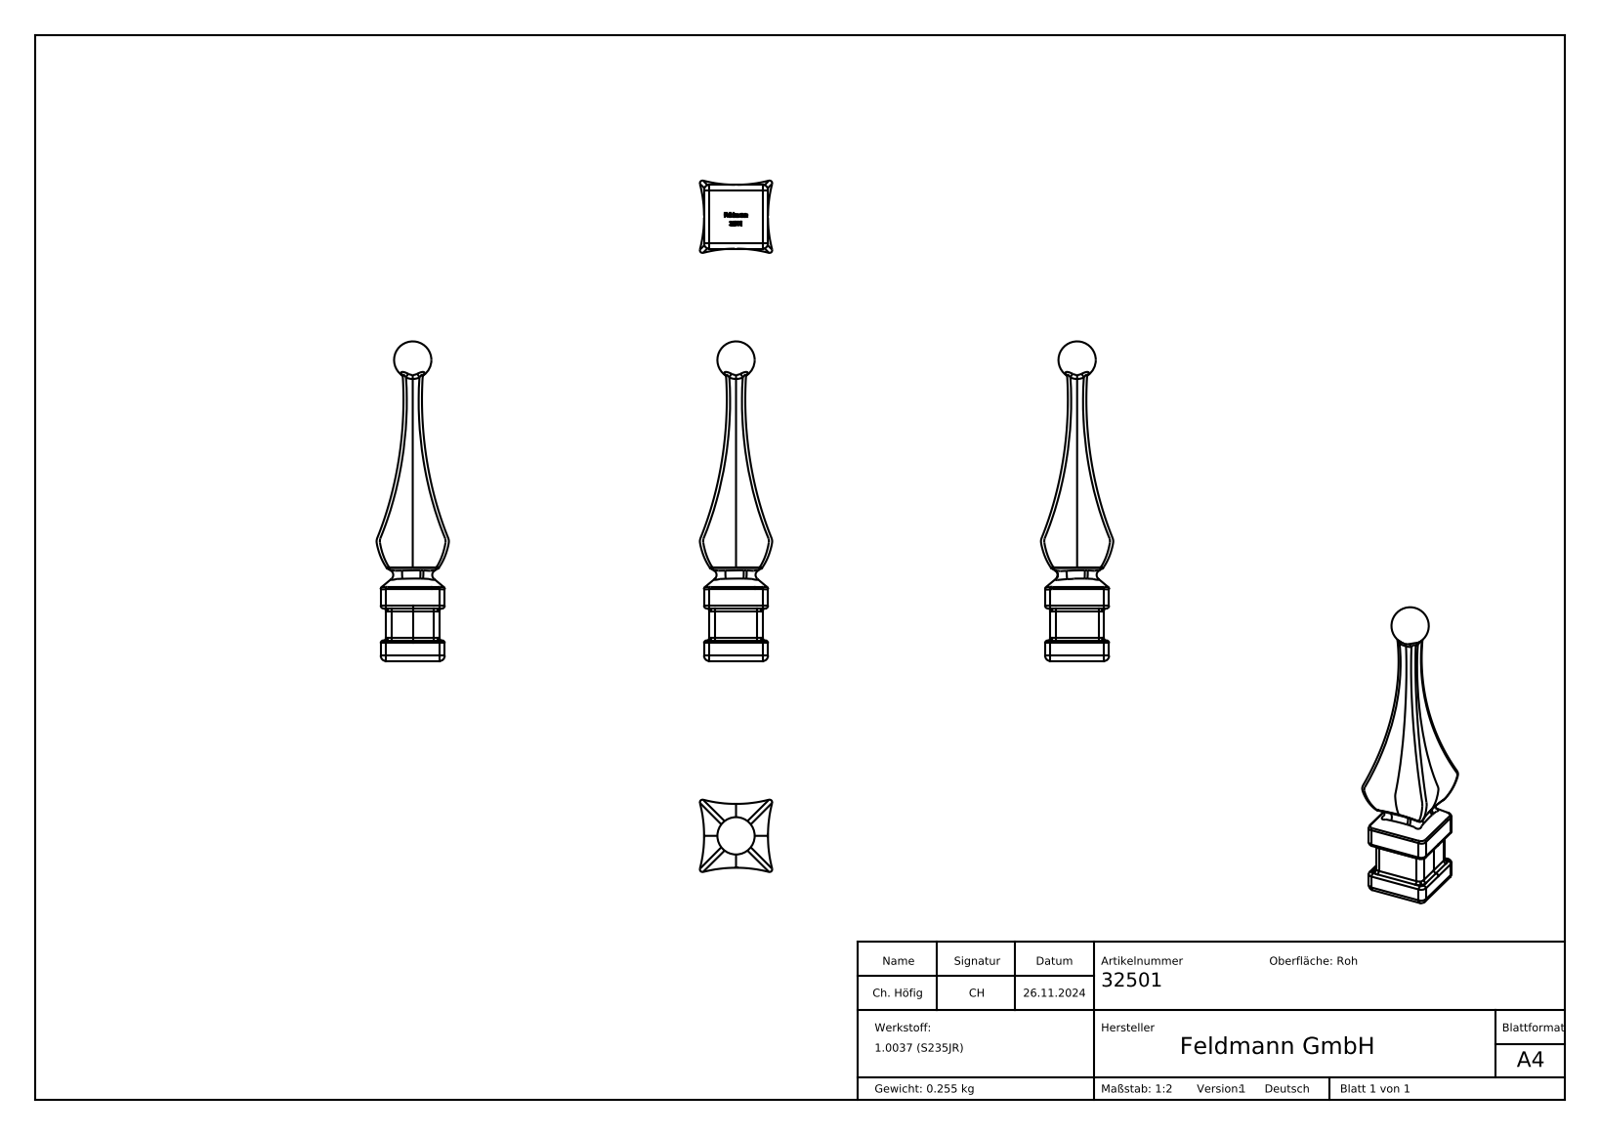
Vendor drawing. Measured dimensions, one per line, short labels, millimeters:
name: 32501
written by: SolidWorks 2018 (CONFIG_CONTROL_DESIGN)
unit: mm
bodies: 1 solid, 376 faces (130 planar, 36 cylindrical, 210 other)
size: 120 × 27.15 × 27.15
volume: 32 894 mm³; area: 8 562 mm²
rounds: 16× R1, 12× R2
face distances: 2, 22, 24, 20, 12, 7.75, 19.75, 7.65, 19.65, 10
